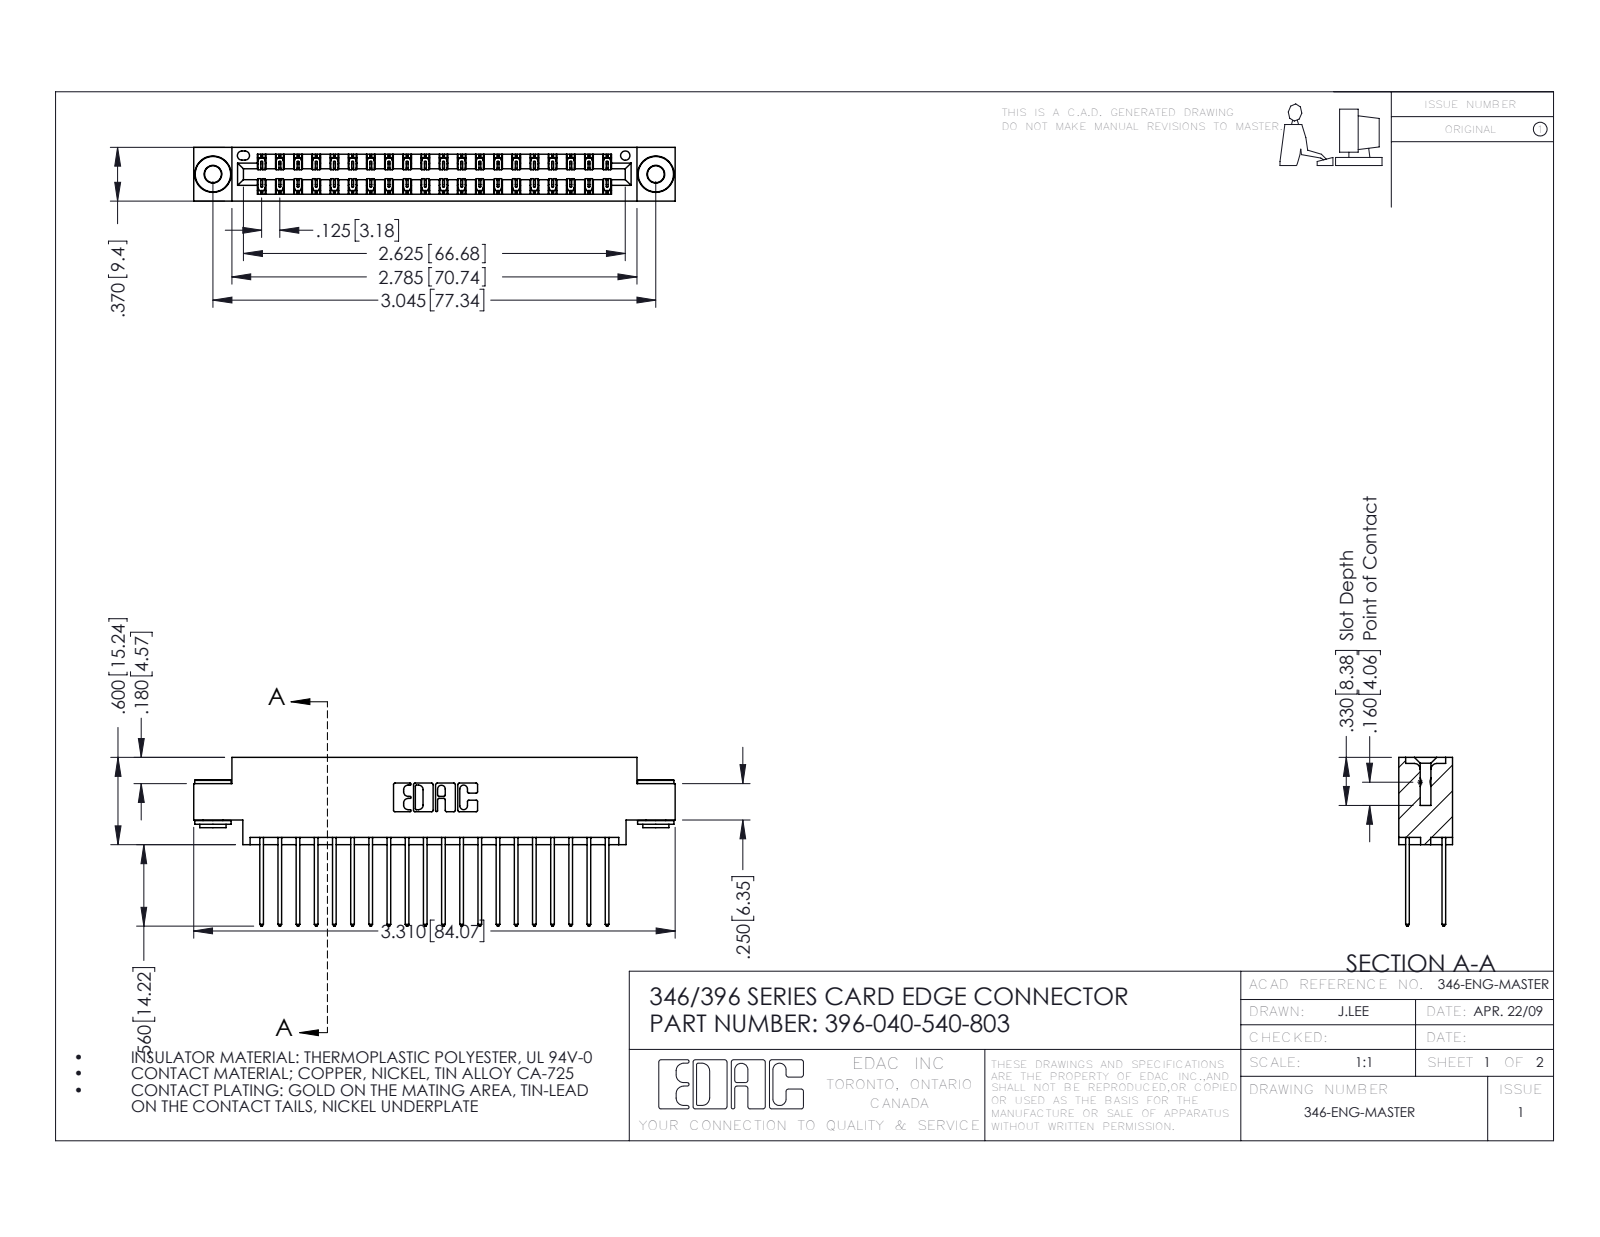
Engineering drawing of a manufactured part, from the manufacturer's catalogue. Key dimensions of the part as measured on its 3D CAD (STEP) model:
Part name (STEP PRODUCT): 346 Part_0.170 Offset - 0.156 Dia-TH; 396-040-540-803; 345-292-001_345-293-140; 345-250-002_345-250-002-102
STEP written by: SolidWorks 2016 (CONFIG_CONTROL_DESIGN)
Units: inches
Bodies: 43 solids, 2244 faces (1490 planar, 746 cylindrical, 8 other)
Overall size (bounding box): 3.31 × 1.16 × 0.37
Volume: 0.491 in³ · Surface area: 18.32 in²
Round holes (diameter × count): ⌀0.116 ×2, ⌀0.156 ×2, ⌀0.064 ×1
Round bosses / shafts (diameter × count): ⌀0.25 ×2, ⌀0.18 ×2, ⌀0.136 ×2
Partial cylindrical surfaces — rounded edges, fillets, slot ends (radius × count): R0.006 ×60, R0.01 ×40, R0.01 ×22, R0.007 ×6, R0.031 ×6, R0.026 ×3, R0.014 ×2, R0.022 ×2
Main face-to-face distances: 0.048, 0.322, 0.25, 0.37, 0.025, 0.072, 0.298, 0.275, 0.148, 0.222
Hole centre spacings: 0.246, 2.837, 3.045
